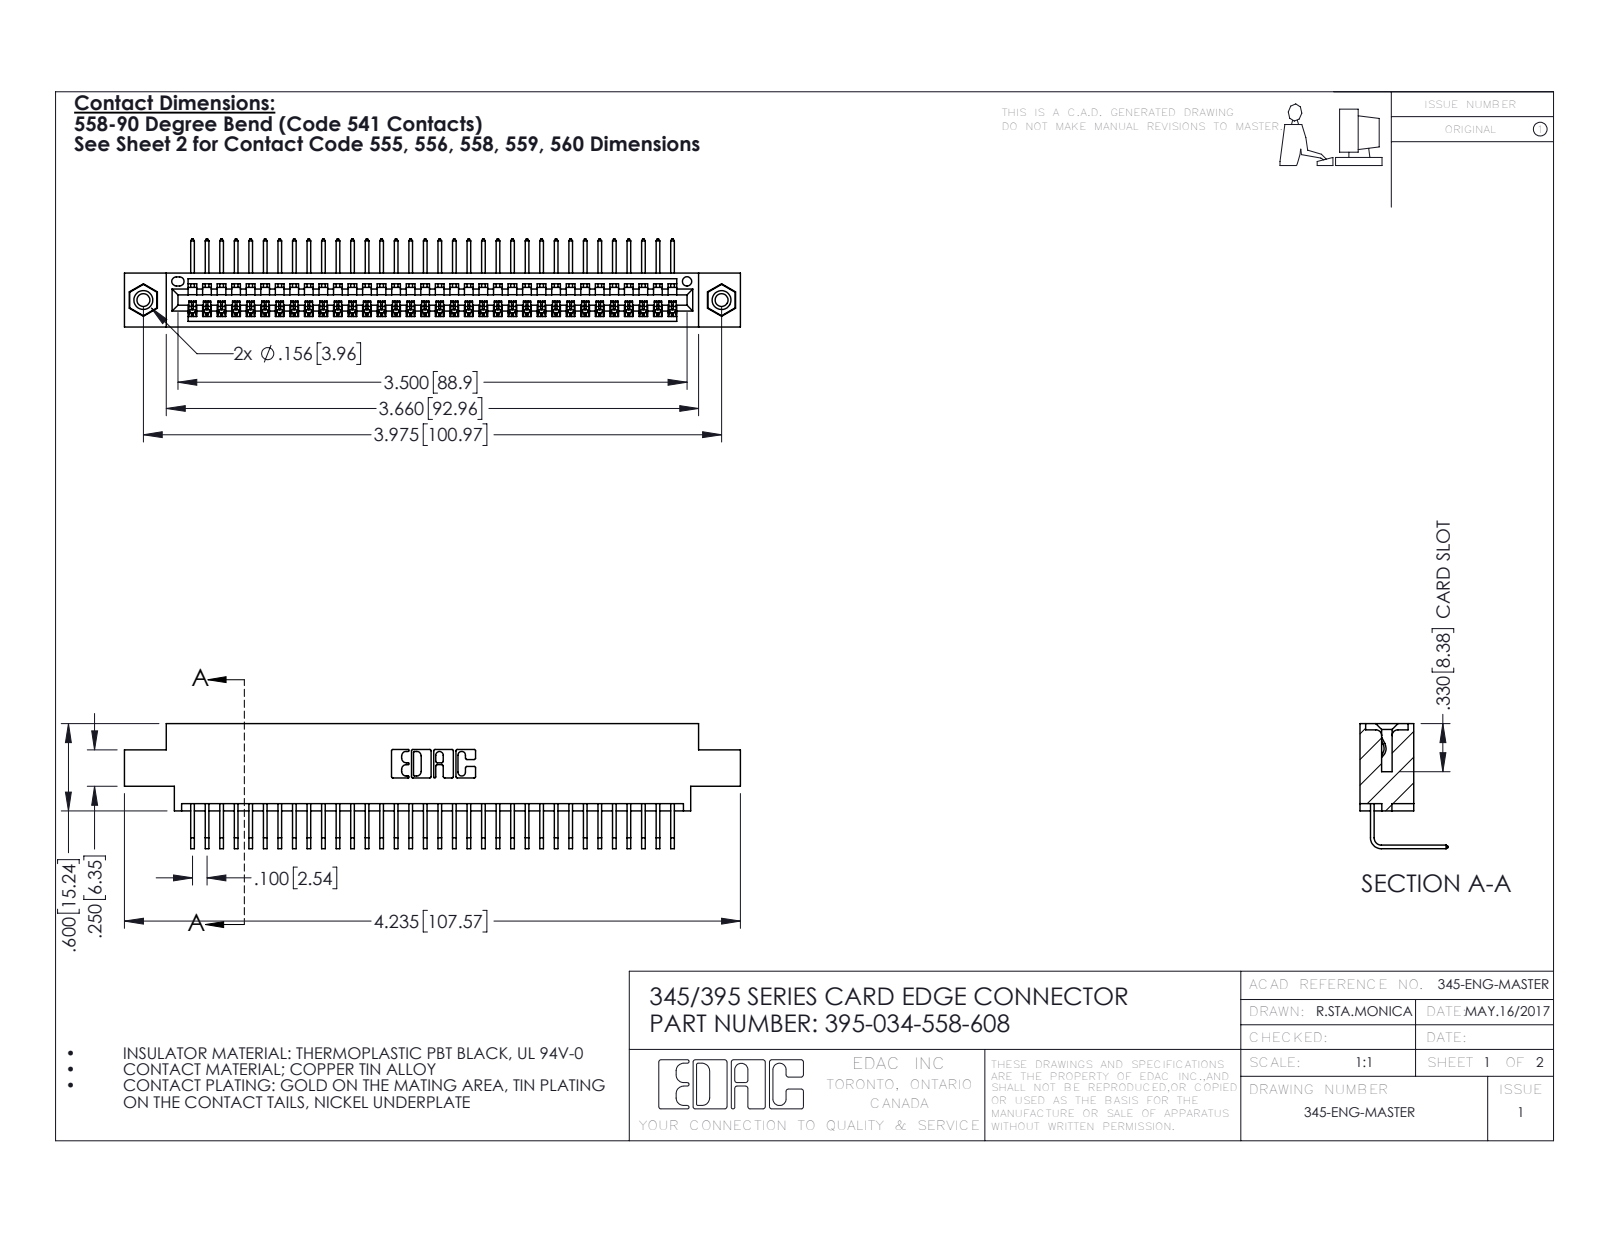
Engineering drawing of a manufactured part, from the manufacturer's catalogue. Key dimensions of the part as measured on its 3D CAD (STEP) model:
Part name (STEP PRODUCT): 345-292-001_558 Tail - 2; 345 Part_0.170 Offset - 0.156 Dia-TI; 345-250-001_345-250-003-102; 395-034-558-608
STEP written by: SolidWorks 2016 (CONFIG_CONTROL_DESIGN)
Units: inches
Bodies: 37 solids, 2230 faces (1544 planar, 670 cylindrical, 16 other)
Overall size (bounding box): 4.235 × 0.859 × 0.605
Volume: 0.619 in³ · Surface area: 21.99 in²
Round holes (diameter × count): ⌀0.089 ×2, ⌀0.125 ×2, ⌀0.156 ×2, ⌀0.064 ×1
Round bosses / shafts (diameter × count): ⌀0.155 ×2
Partial cylindrical surfaces — rounded edges, fillets, slot ends (radius × count): R0.006 ×68, R0.01 ×22, R0.007 ×6, R0.031 ×6, R0.026 ×3, R0.031 ×2, R0.04 ×2, R0.014 ×1
Main face-to-face distances: 0.072, 0.298, 0.37, 0.2, 0.098, 0.272, 0.025, 0.225, 0.175, 0.149
Hole centre spacings: 0.27, 3.74, 3.975
